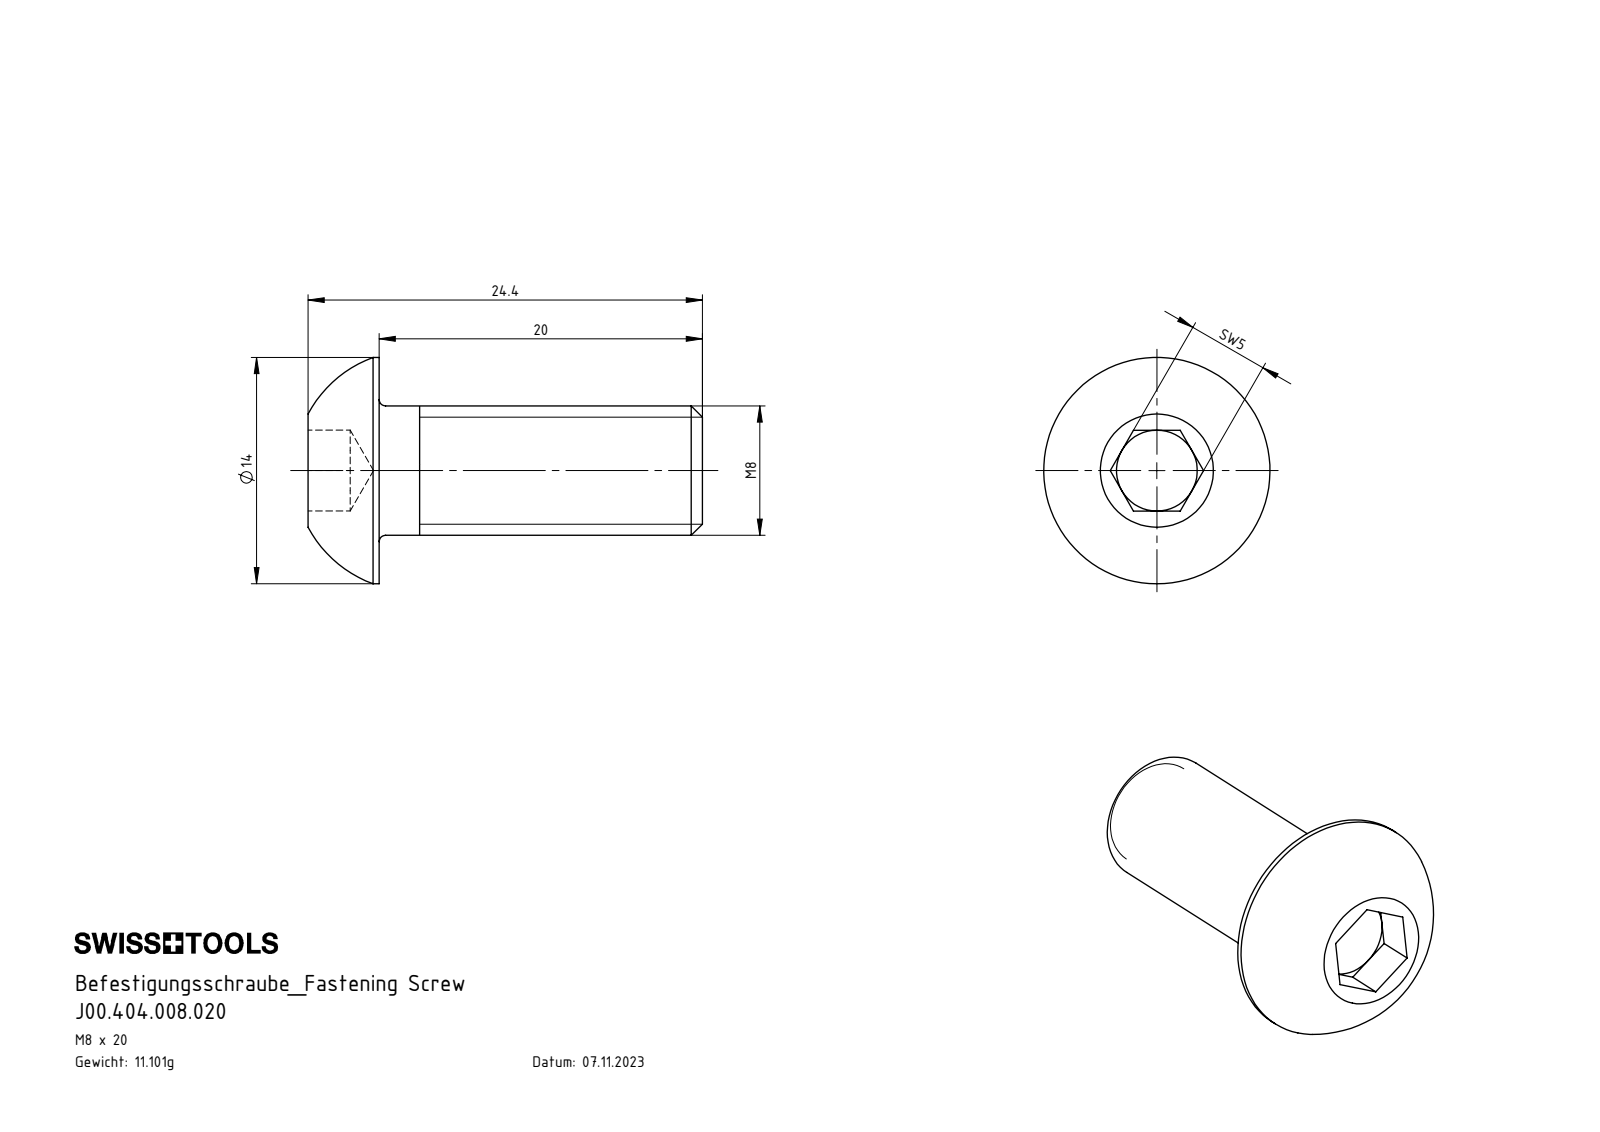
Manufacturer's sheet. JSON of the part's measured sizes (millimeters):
{"part_name": "J00.404.008.020", "step_written_by": "SolidWorks 2022 (AUTOMOTIVE_DESIGN)", "units": "millimeters", "bodies": {"solids": 1, "faces": 27, "planar": 15, "cylindrical": 4, "other": 8}, "overall_size": [24.4, 14, 14], "volume_mm3": 1414, "surface_area_mm2": 933, "round_bosses_or_shafts": [[14, 1], [8, 1]], "face_to_face_distances": [20, 5, 4.4, 24.4, 2.6, 1.8, 21.8]}
